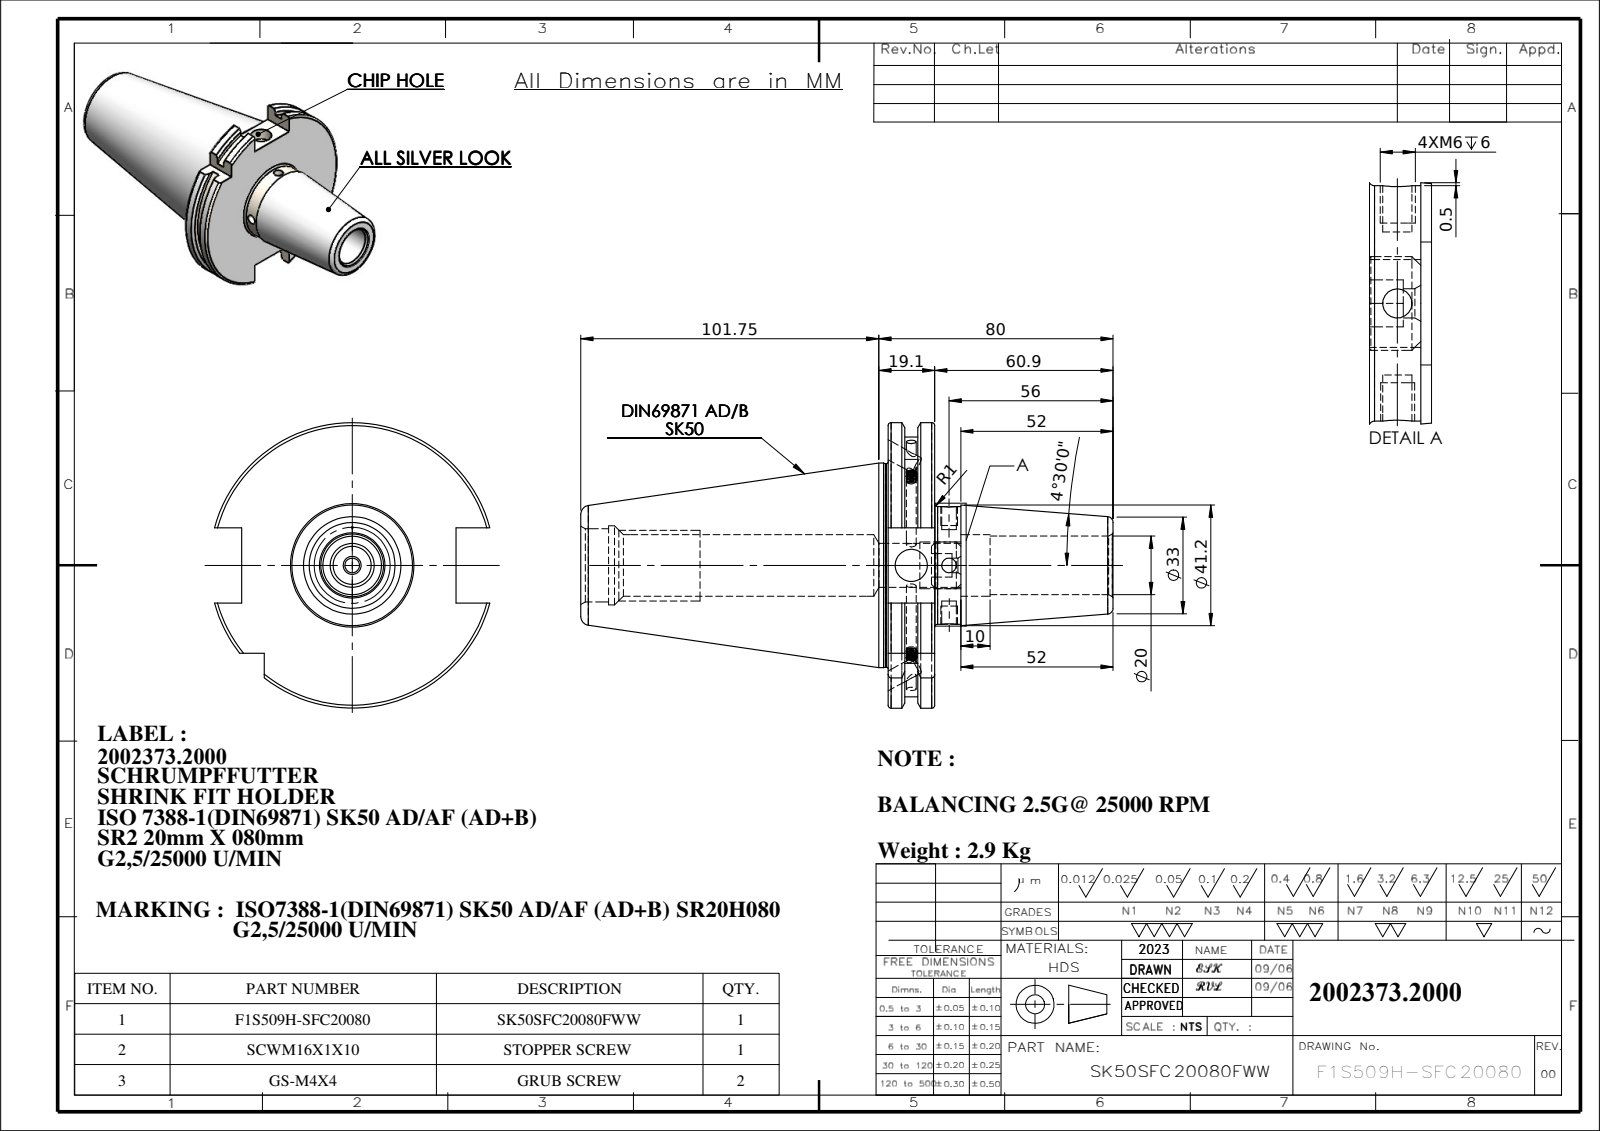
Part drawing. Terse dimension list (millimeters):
name: SK50SFC20080FWW; 91506-SR220080; GS-M4X4_DIN 913 - M4 x 4-N; SCWM16X1X10
written by: SolidWorks 2018 (CONFIG_CONTROL_DESIGN)
unit: mm
bodies: 4 solids, 238 faces (57 planar, 77 cylindrical, 104 other)
size: 181.75 × 97.5 × 94.05
volume: 371 273 mm³; area: 56 968 mm²
holes: 3× ⌀5, 2× ⌀6, 1× ⌀3.3, 1× ⌀11, 1× ⌀15, 1× ⌀20, 1× ⌀21, 1× ⌀25, 1× ⌀27
bosses: 2× ⌀4, 1× ⌀69.85, 1× ⌀69.45, 1× ⌀40.18, 1× ⌀16
rounds: 1× R44.9, 1× R48.75
face distances: 15.9, 5.65, 10.25, 10.14, 4.49, 5.76, 104.95, 110.6, 115.09, 120.85
hole spacings: 12.9
